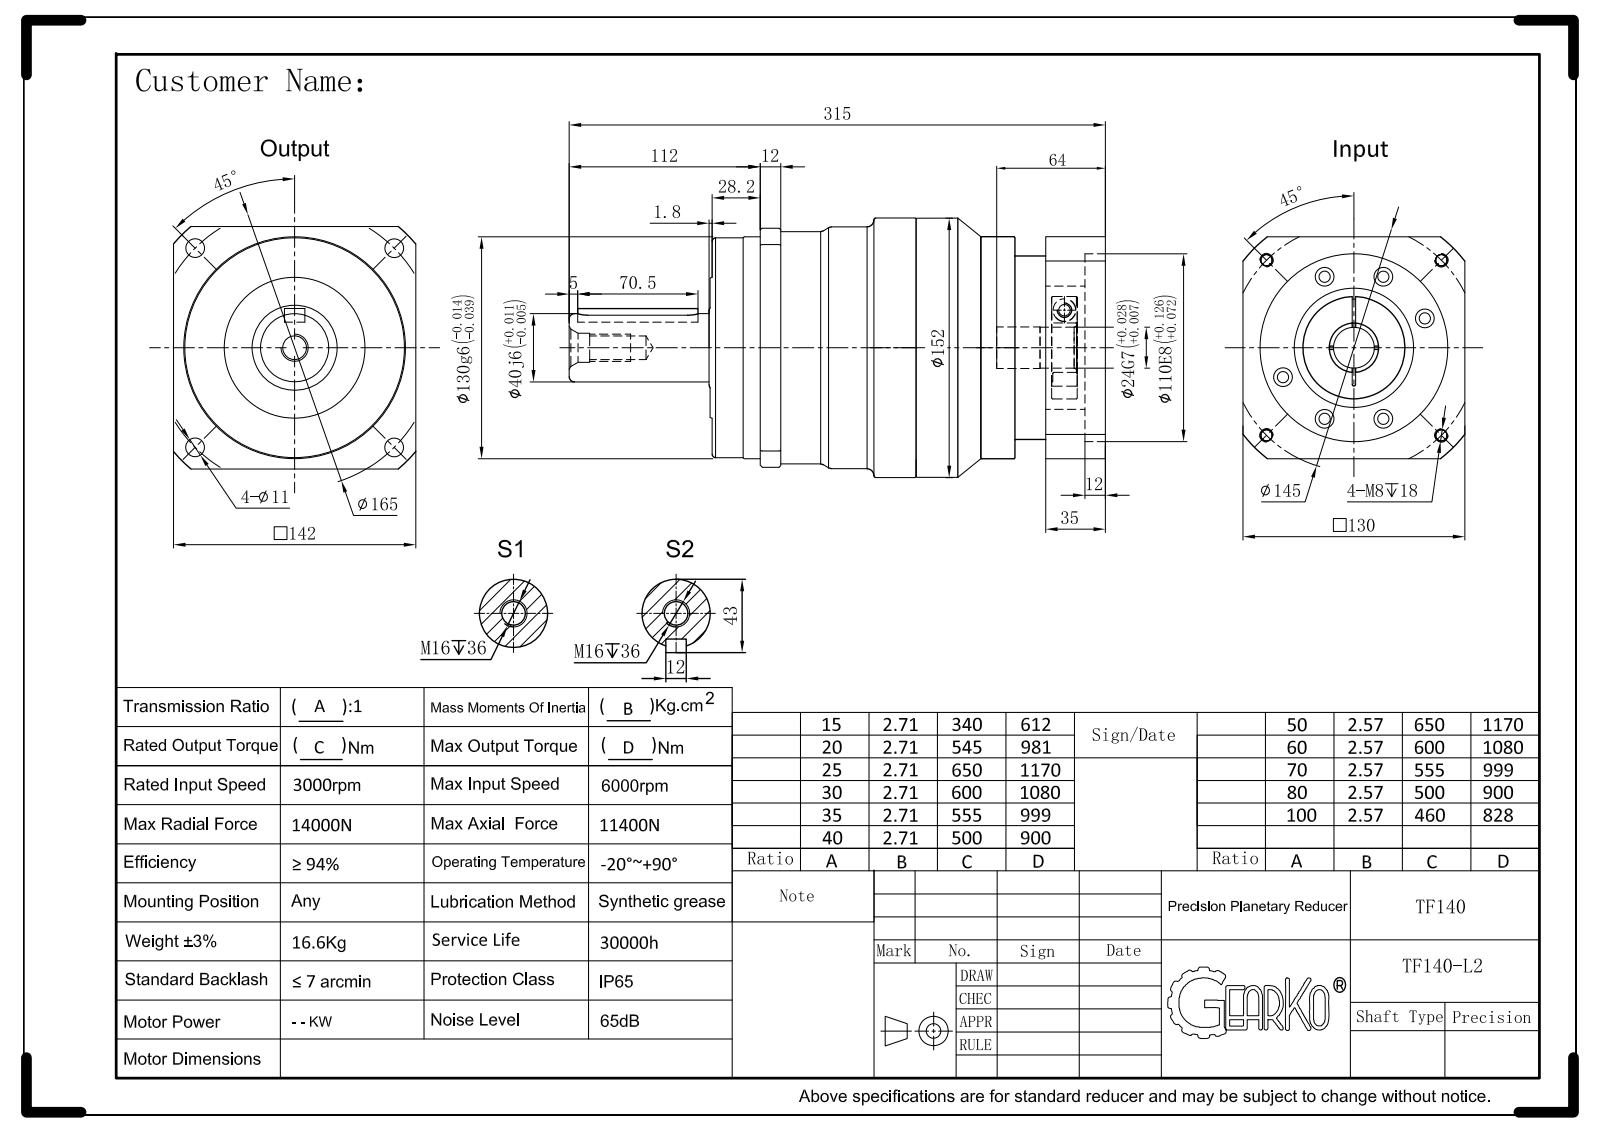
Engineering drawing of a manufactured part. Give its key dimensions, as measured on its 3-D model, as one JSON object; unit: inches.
{"part_name": "TF140-L2-24-110-145-M8-64-12", "step_written_by": "SolidWorks 2017 (CONFIG_CONTROL_DESIGN)", "units": "inches", "bodies": {"solids": 4, "faces": 197, "planar": 50, "cylindrical": 81, "other": 66}, "overall_size": [12.374, 5.984, 5.984], "volume_in3": 211.1, "surface_area_in2": 330.9, "round_holes": [[0.268, 4], [0.433, 4], [0.524, 1], [0.551, 1], [0.63, 1], [0.669, 1], [0.945, 1], [1.142, 1], [1.583, 1], [1.969, 1], [2.756, 1], [3.937, 1]], "round_bosses_or_shafts": [[5.984, 1], [5.571, 1], [5.354, 1], [5.118, 1], [5.071, 1], [4.232, 1], [2.362, 1], [1.575, 1]], "partial_cylinders_radius": [[0.02, 4], [0.236, 3], [0.039, 1], [3.248, 1], [3.642, 1]], "face_to_face_distances": [0.472, 7.492, 7.815, 7.697, 0.118, 1.26, 5.118, 9.075, 1.378, 1.11], "hole_center_spacings": [0.394, 4.324, 4.324, 6.102, 2.854, 2.855, 3.248, 3.248]}
